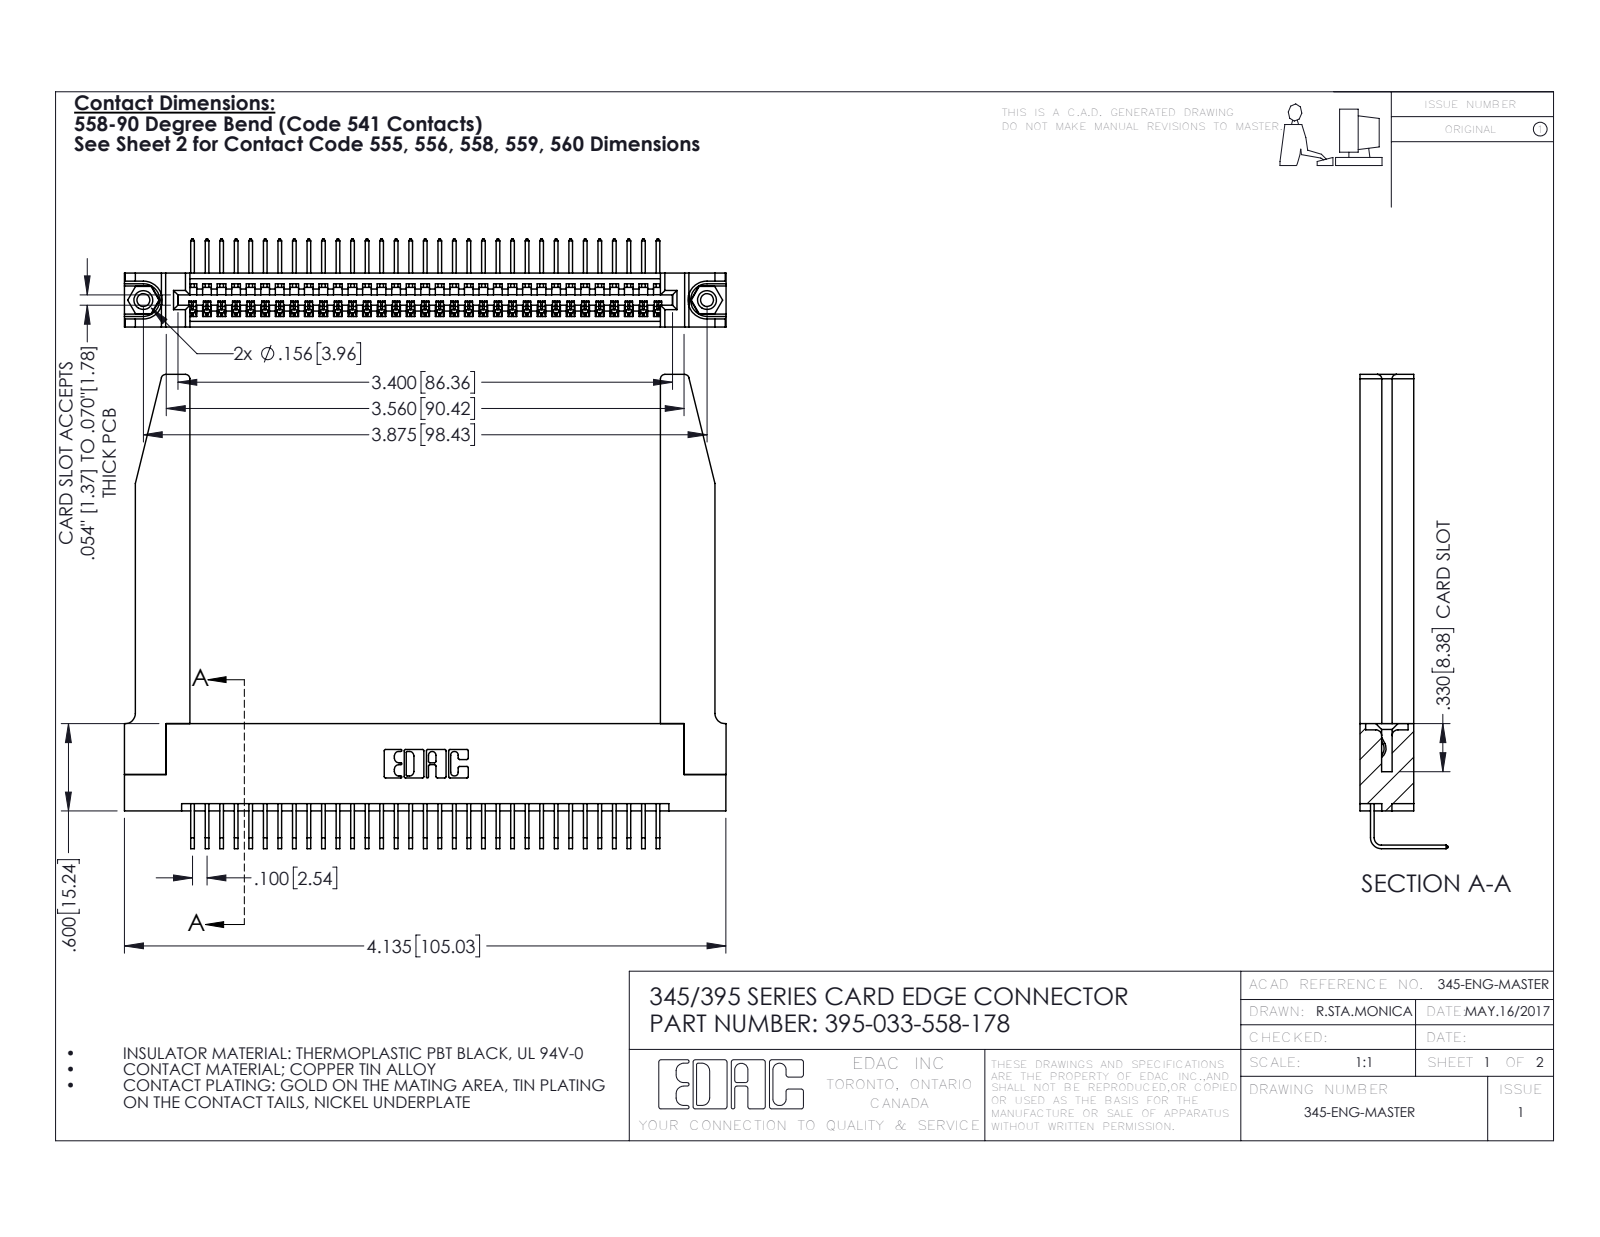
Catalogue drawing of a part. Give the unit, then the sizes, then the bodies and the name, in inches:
Units: inches
Overall size (bounding box): 4.136 × 3.259 × 0.605
Round holes (diameter × count): ⌀0.089 ×2, ⌀0.125 ×2, ⌀0.156 ×2, ⌀0.064 ×1
Round bosses / shafts (diameter × count): ⌀0.155 ×2
Partial cylindrical surfaces — rounded edges, fillets, slot ends (radius × count): R0.006 ×66, R0.01 ×22, R0.03 ×8, R0.007 ×6, R0.031 ×6, R0.026 ×3, R0.031 ×2, R0.04 ×2
Main face-to-face distances: 0.37, 0.072, 0.298, 0.2, 0.098, 0.272, 0.025, 0.148, 0.15, 0.225
Hole centre spacings: 0.27, 3.64, 3.875
Volume: 1.085 in³ · Surface area: 32.05 in²
Bodies: 38 solids, 2340 faces (1608 planar, 680 cylindrical, 52 other)
Part name (STEP PRODUCT): 345-250-001_345-250-001-102; 345-220-078_345-220-078; 395-033-558-178; 345-292-001_558 Tail - 2 (+1 more)
STEP written by: SolidWorks 2016 (CONFIG_CONTROL_DESIGN)
